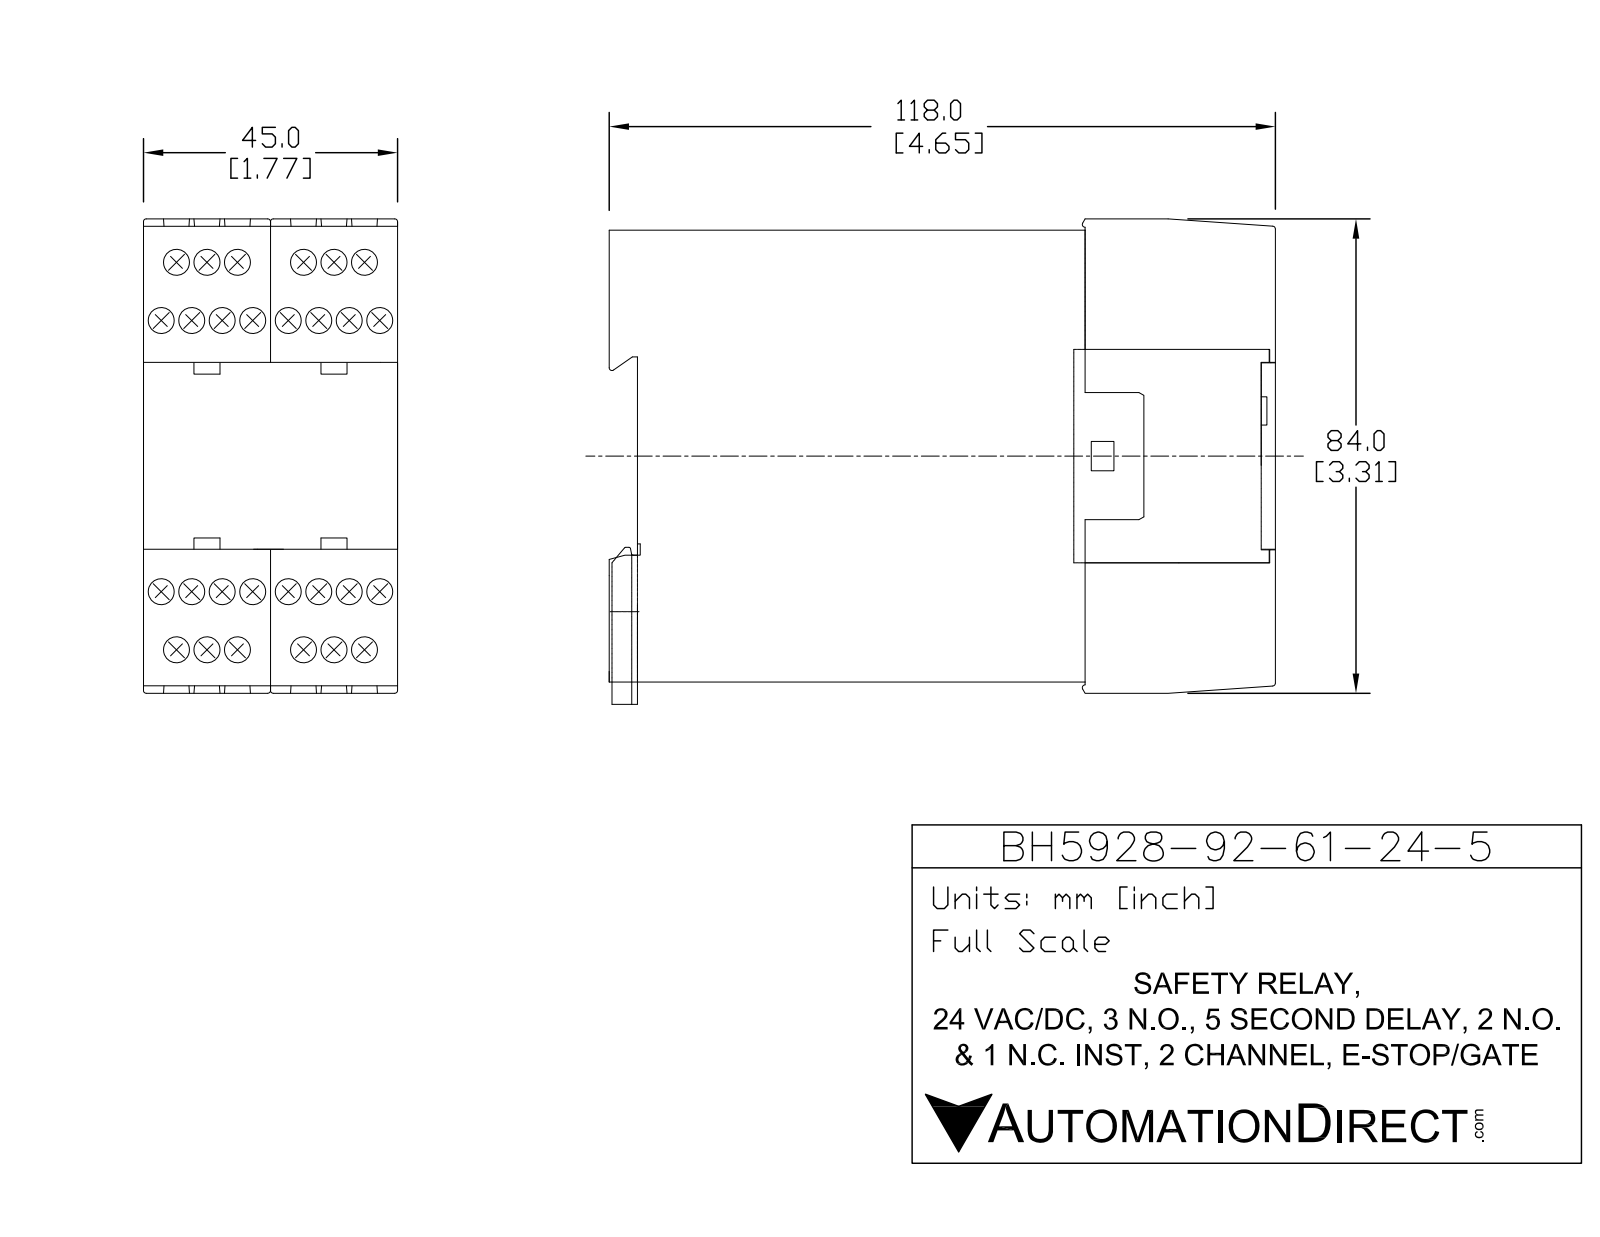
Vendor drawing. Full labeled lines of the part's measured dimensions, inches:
Part name (STEP PRODUCT): BH5928-92-61-24-1
STEP written by: SolidWorks 2017 (AUTOMOTIVE_DESIGN)
Units: inches
Bodies: 1 solid, 1533 faces (1034 planar, 369 cylindrical, 130 other)
Overall size (bounding box): 4.654 × 3.346 × 1.772
Volume: 24.87 in³ · Surface area: 74.68 in²
Round holes (diameter × count): ⌀0.181 ×28, ⌀0.315 ×2
Round bosses / shafts (diameter × count): ⌀0.087 ×1
Partial cylindrical surfaces — rounded edges, fillets, slot ends (radius × count): R0.02 ×133, R0.008 ×64, R0.059 ×32, R0.049 ×8, R0.079 ×3, R0.012 ×2, R0.043 ×1, R0.085 ×1
Main face-to-face distances: 1.772, 3.15, 1.77, 4.449, 0.079, 3.071, 1.768, 0.037, 2.992, 0.884
Hole centre spacings: 0.419, 2.306, 0.213, 0.516, 2.325, 0.886, 0.425, 0.879
